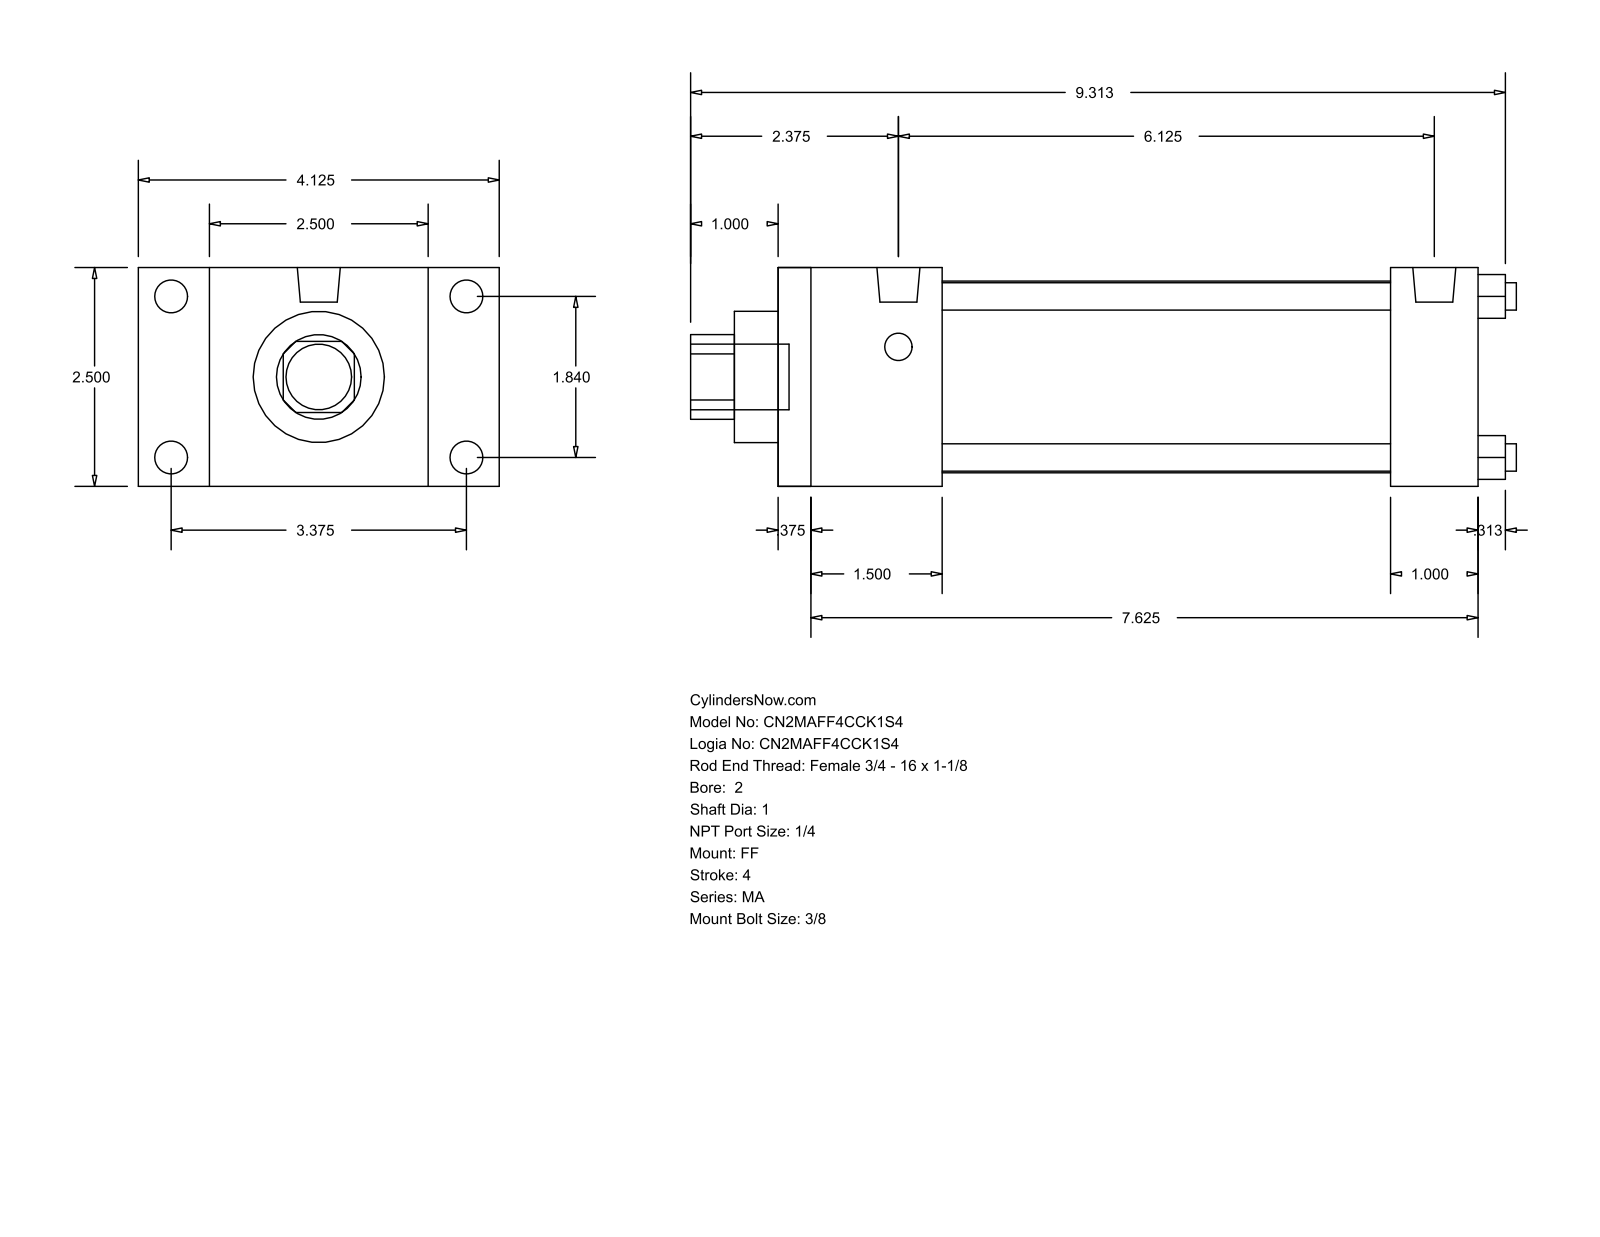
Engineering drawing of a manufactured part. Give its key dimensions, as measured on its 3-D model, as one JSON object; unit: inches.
{"part_name": "MA_FF__0200_1", "step_written_by": "GSSL Pune (CONFIG_CONTROL_DESIGN)", "units": "inches", "bodies": {"solids": 0, "faces": 92, "planar": 64, "cylindrical": 28, "other": 0}, "overall_size": [9.437, 4.125, 2.5], "round_holes": [[0.313, 4], [1, 1], [1.5, 1], [2.19, 1]], "round_bosses_or_shafts": [[0.375, 4], [0.313, 4], [0.492, 2], [0.75, 1]], "partial_cylinders_radius": [[0.484, 1]], "face_to_face_distances": [2.5, 8, 0.375, 7.625, 1, 0.813, 0.5, 1.875, 7, 1.5], "hole_center_spacings": [1.301, 1.84, 2.602]}
